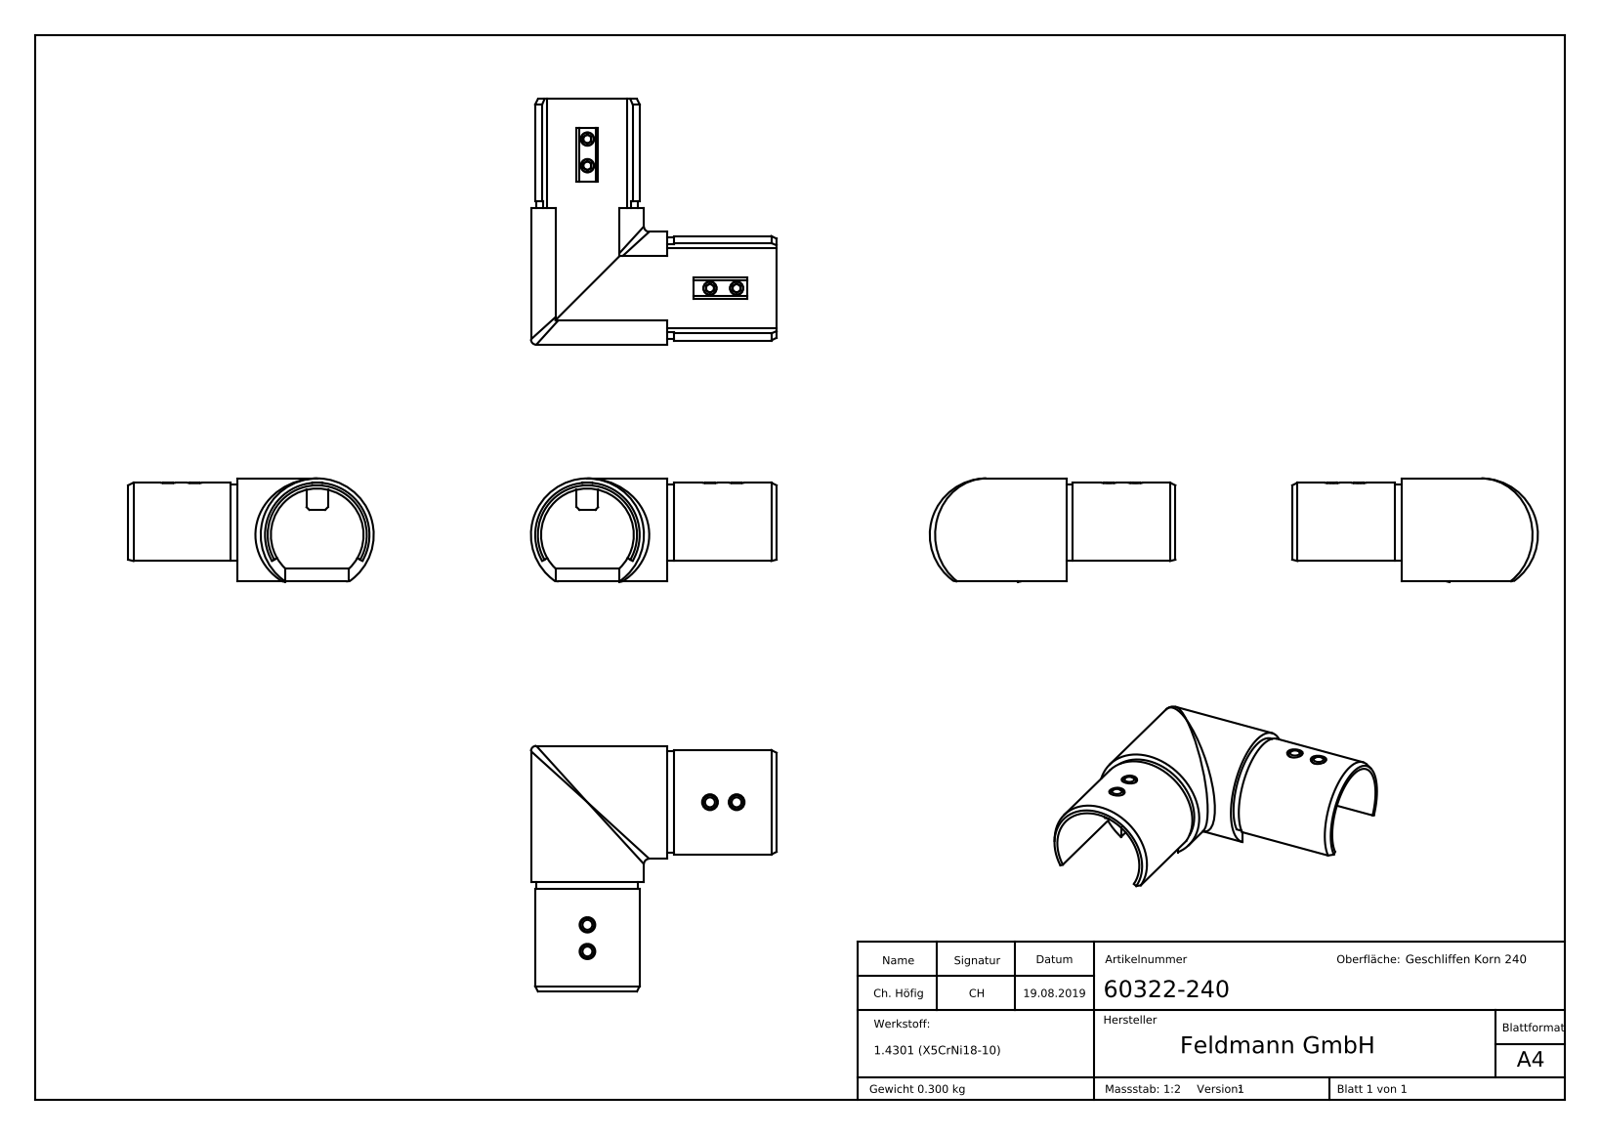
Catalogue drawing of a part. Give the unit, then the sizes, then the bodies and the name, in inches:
Units: inches
Overall size (bounding box): 3.63 × 3.63 × 1.53
Round holes (diameter × count): ⌀0.197 ×4
Round bosses / shafts (diameter × count): ⌀0.236 ×4, ⌀1.669 ×2
Partial cylindrical surfaces — rounded edges, fillets, slot ends (radius × count): R0.685 ×2, R0.752 ×2, R0.772 ×2
Main face-to-face distances: 0.315, 0.63, 1.654, 1.339, 1.024, 2.323, 3.268, 2.953, 2.638, 1.614
Hole centre spacings: 0.394, 2.853, 2.561, 3.118
Volume: 2.317 in³ · Surface area: 43.55 in²
Bodies: 5 solids, 390 faces (203 planar, 40 cylindrical, 147 other)
Part name (STEP PRODUCT): 6032X-240 Teil1 Konfig Verlaufecke Nutrohr_60322-240 Teil1; 60322-240; DIN913_DIN 913 M6x10
STEP written by: SolidWorks 2015 (CONFIG_CONTROL_DESIGN)
